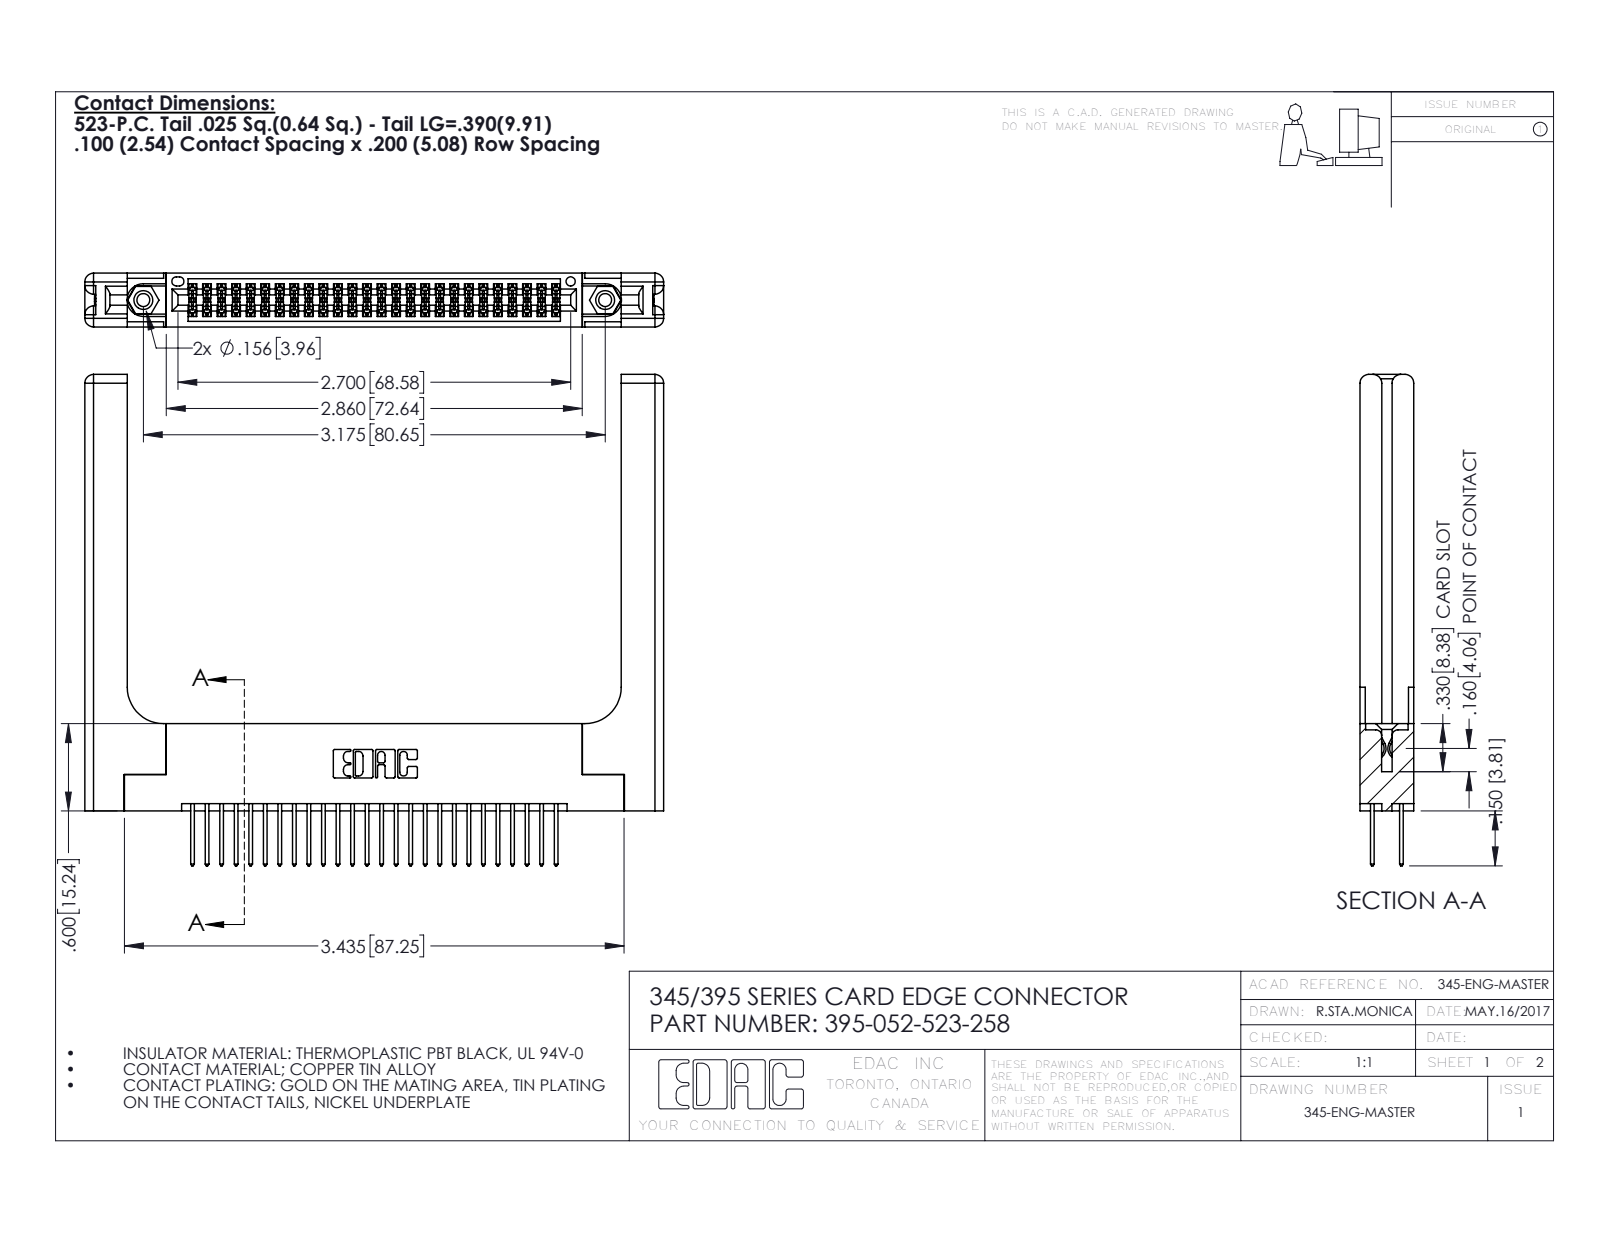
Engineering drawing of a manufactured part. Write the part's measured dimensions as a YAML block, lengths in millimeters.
part_name: "395-052-523-258; 345-250-001_345-250-001-102; 345-220-058_345-220-058; 345-292-001_345-293-123 (+1 more)"
step_written_by: "SolidWorks 2016 (CONFIG_CONTROL_DESIGN)"
units: millimeters
bodies: {solids: 57, faces: 2982, planar: 1944, cylindrical: 978, other: 60}
overall_size: [101.1, 85.8, 9.4]
volume: 18260
surface_area: 19680
round_holes:
  - {diameter: 2.3, count: 2}
  - {diameter: 3.2, count: 2}
  - {diameter: 4, count: 2}
  - {diameter: 1.6, count: 1}
round_bosses_or_shafts:
  - {diameter: 3.9, count: 2}
partial_cylinders:
  - {radius: 0.2, count: 78}
  - {radius: 0.3, count: 52}
  - {radius: 0.3, count: 22}
  - {radius: 1.5, count: 16}
  - {radius: 0.2, count: 6}
  - {radius: 0.8, count: 6}
  - {radius: 0.7, count: 3}
  - {radius: 0.4, count: 2}
face_to_face_distances: [1.8, 9.4, 7.6, 5.1, 2.5, 6.9, 0.6, 5.7, 3.8, 3.8]
hole_center_spacings: [6.9, 74.7, 80.6]
